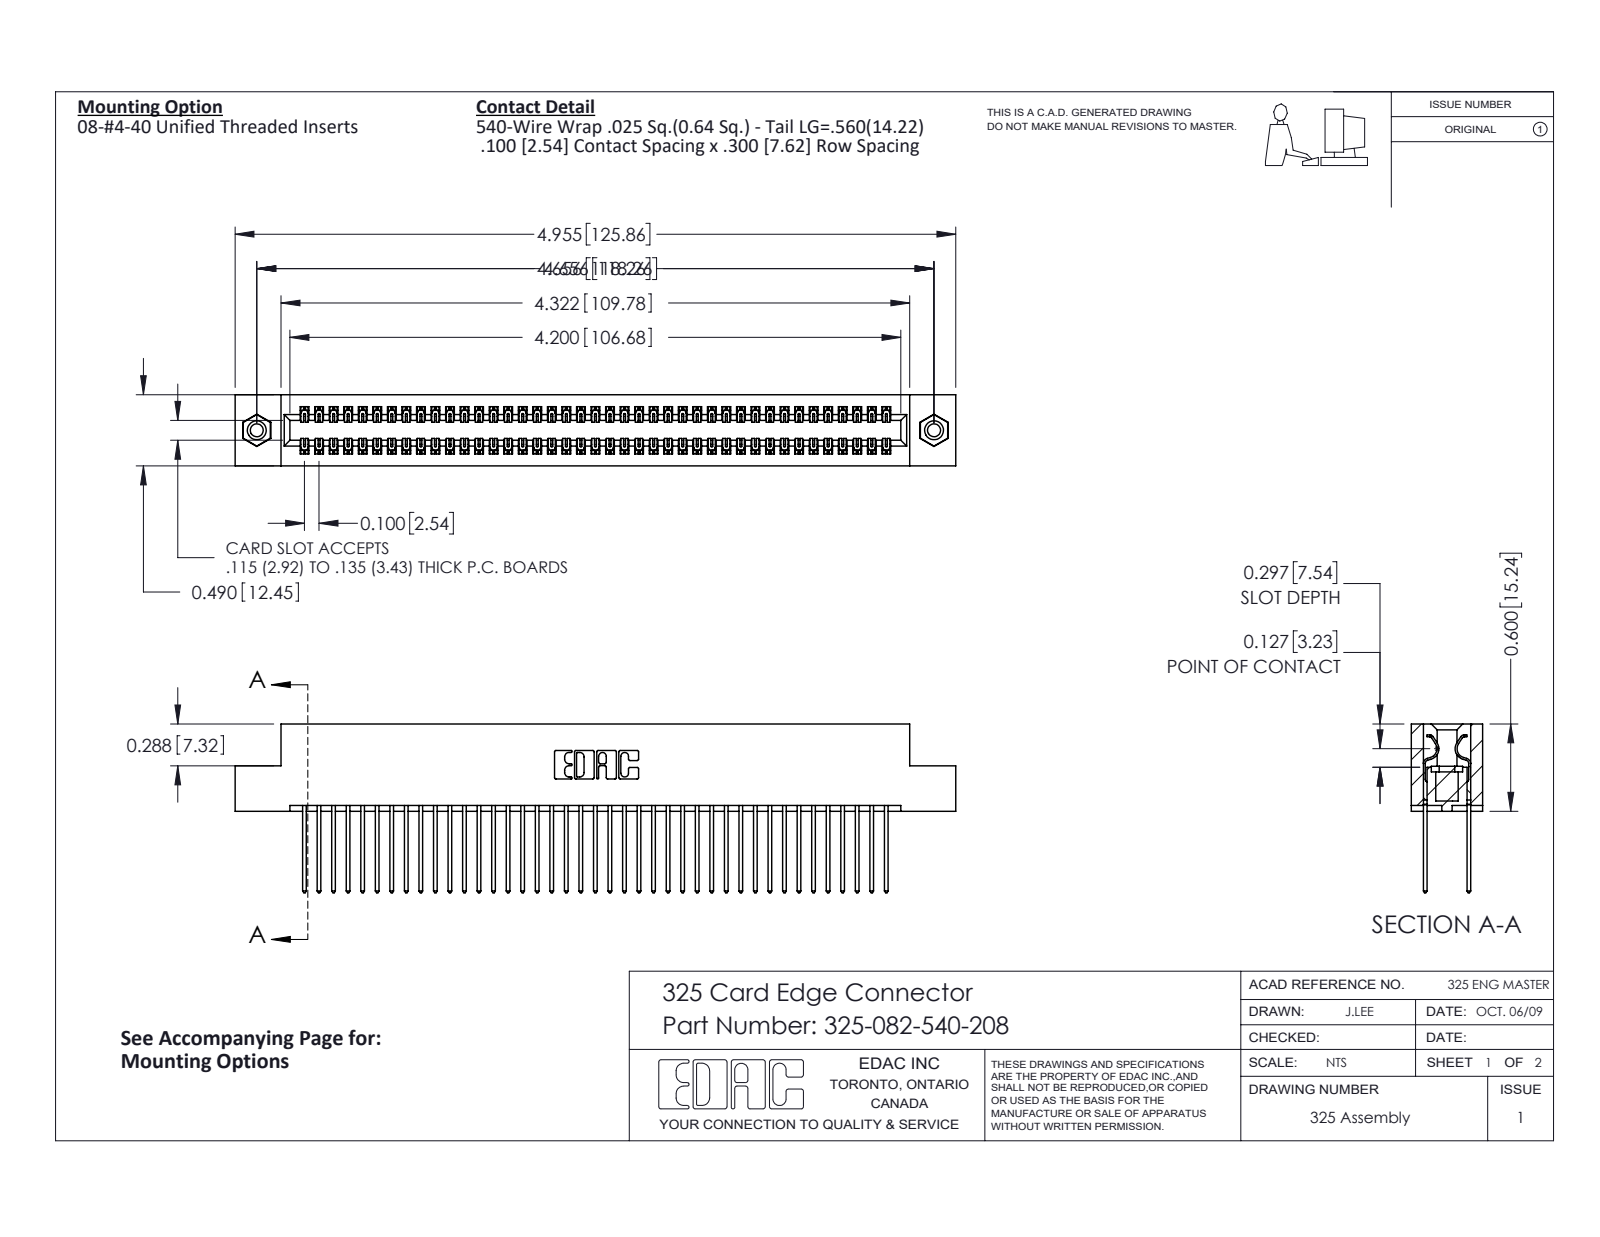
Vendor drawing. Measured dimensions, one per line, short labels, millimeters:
name: 345-250-001_345-250-003-102; 325-292-001_325-293-140; 325 Part_TI; 325-082-540-208
written by: SolidWorks 2016 (CONFIG_CONTROL_DESIGN)
unit: mm
bodies: 85 solids, 4438 faces (3054 planar, 1368 cylindrical, 16 other)
size: 125.9 × 29.5 × 12.4
volume: 16 550 mm³; area: 21 490 mm²
holes: 2× ⌀2.3, 2× ⌀3.2, 2× ⌀4.1
bosses: 2× ⌀3.9
rounds: 123× R0.2, 82× R0.3, 22× R0.3, 6× R0.2, 6× R0.8, 3× R0.7, 2× R0.4, 2× R0.6
face distances: 2.1, 10.3, 7.6, 2.7, 9.7, 0.6, 12.4, 8.3, 7, 14.2
hole spacings: 118.3
